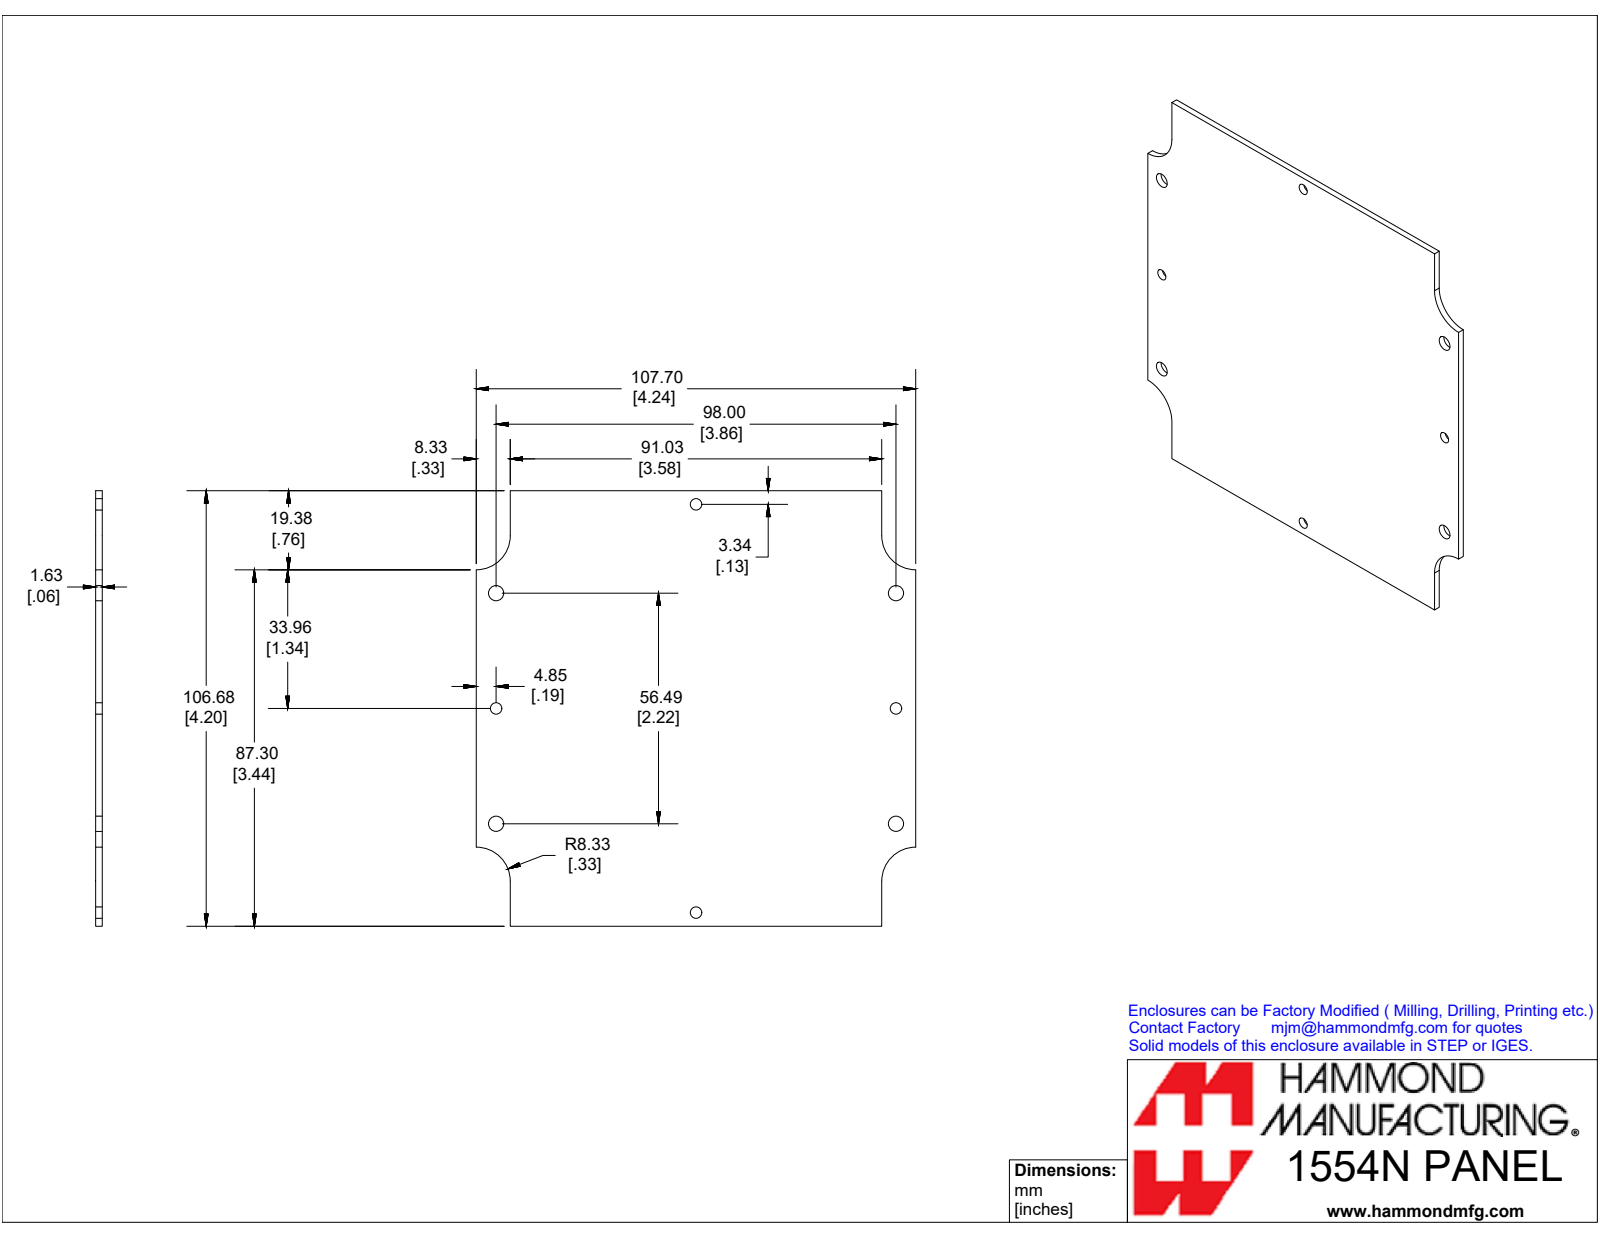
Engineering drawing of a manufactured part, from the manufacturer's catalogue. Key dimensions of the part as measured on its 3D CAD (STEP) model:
Part name (STEP PRODUCT): 1554NPL
STEP written by: SolidWorks 2019 (CONFIG_CONTROL_DESIGN)
Units: inches
Bodies: 1 solid, 22 faces (10 planar, 12 cylindrical, 0 other)
Overall size (bounding box): 4.24 × 4.2 × 0.064
Volume: 1.075 in³ · Surface area: 34.84 in²
Round holes (diameter × count): ⌀0.11 ×4, ⌀0.147 ×4
Partial cylindrical surfaces — rounded edges, fillets, slot ends (radius × count): R0.328 ×4
Main face-to-face distances: 0.064, 4.2, 4.24, 0.328, 3.912, 3.584
Hole centre spacings: 1.112, 2.111, 2.756, 3.635, 4.015, 3.858, 2.224, 4.453
